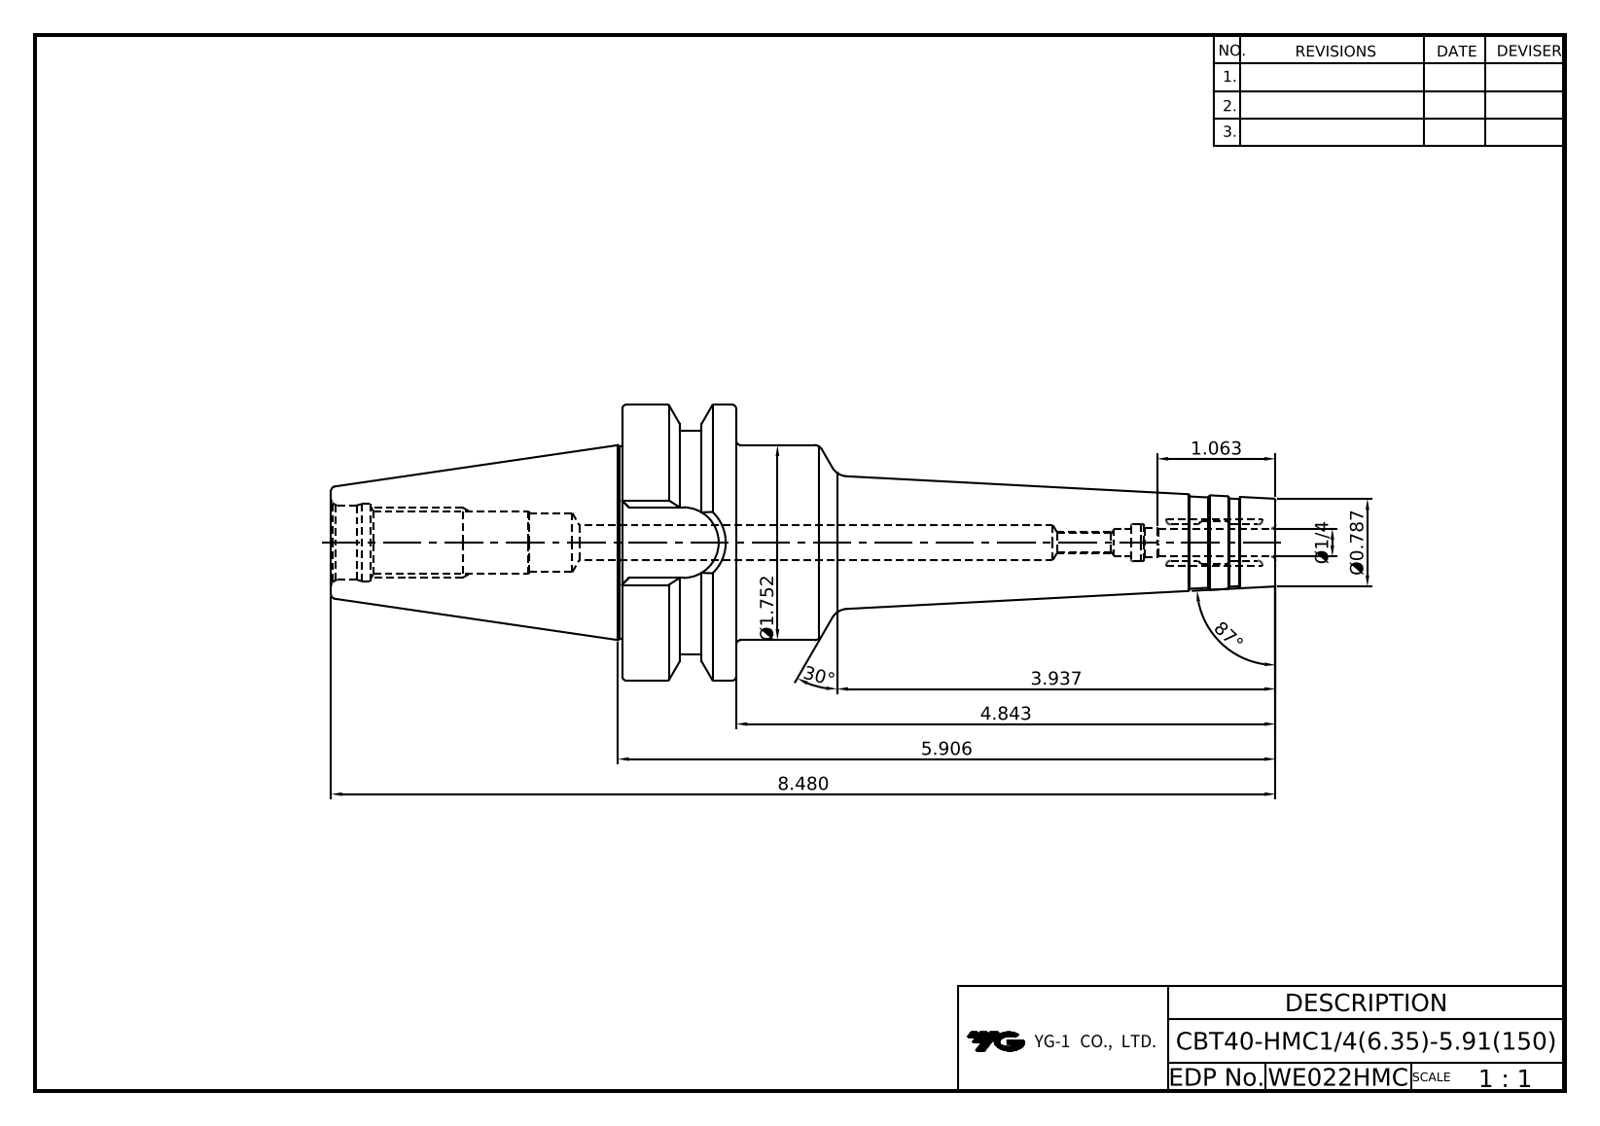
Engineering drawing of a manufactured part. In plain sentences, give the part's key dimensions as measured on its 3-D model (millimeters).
The part is named "CBT40-HMC6.35-150". Its 3-D file was written by "Autodesk Inventor 2022 (AUTOMOTIVE_DESIGN)". It is 1 solid with 87 faces: 25 planar, 18 cylindrical and 44 other. Overall it measures 215.4 by 63 by 63 millimeters. Its volume is 202 044 cubic millimeters and its surface area 35 368 square millimeters. Round holes: 1 of diameter 4.3, 1 of diameter 6.35, 1 of diameter 6.8, 1 of diameter 8, 1 of diameter 12, 1 of diameter 13.5, 1 of diameter 13.84, 1 of diameter 17, 1 of diameter 17.6. Round bosses or shafts: 1 of diameter 63, 1 of diameter 52.6, 1 of diameter 44.5, 1 of diameter 44. Partial cylindrical surfaces (rounded edges, fillets, slot ends): 1 of radius 8.05. The main face-to-face distances are 26, 149, 123, 0.4, 25.6, 148.6, 45.2, 16.1, 66.4, 66.8.
